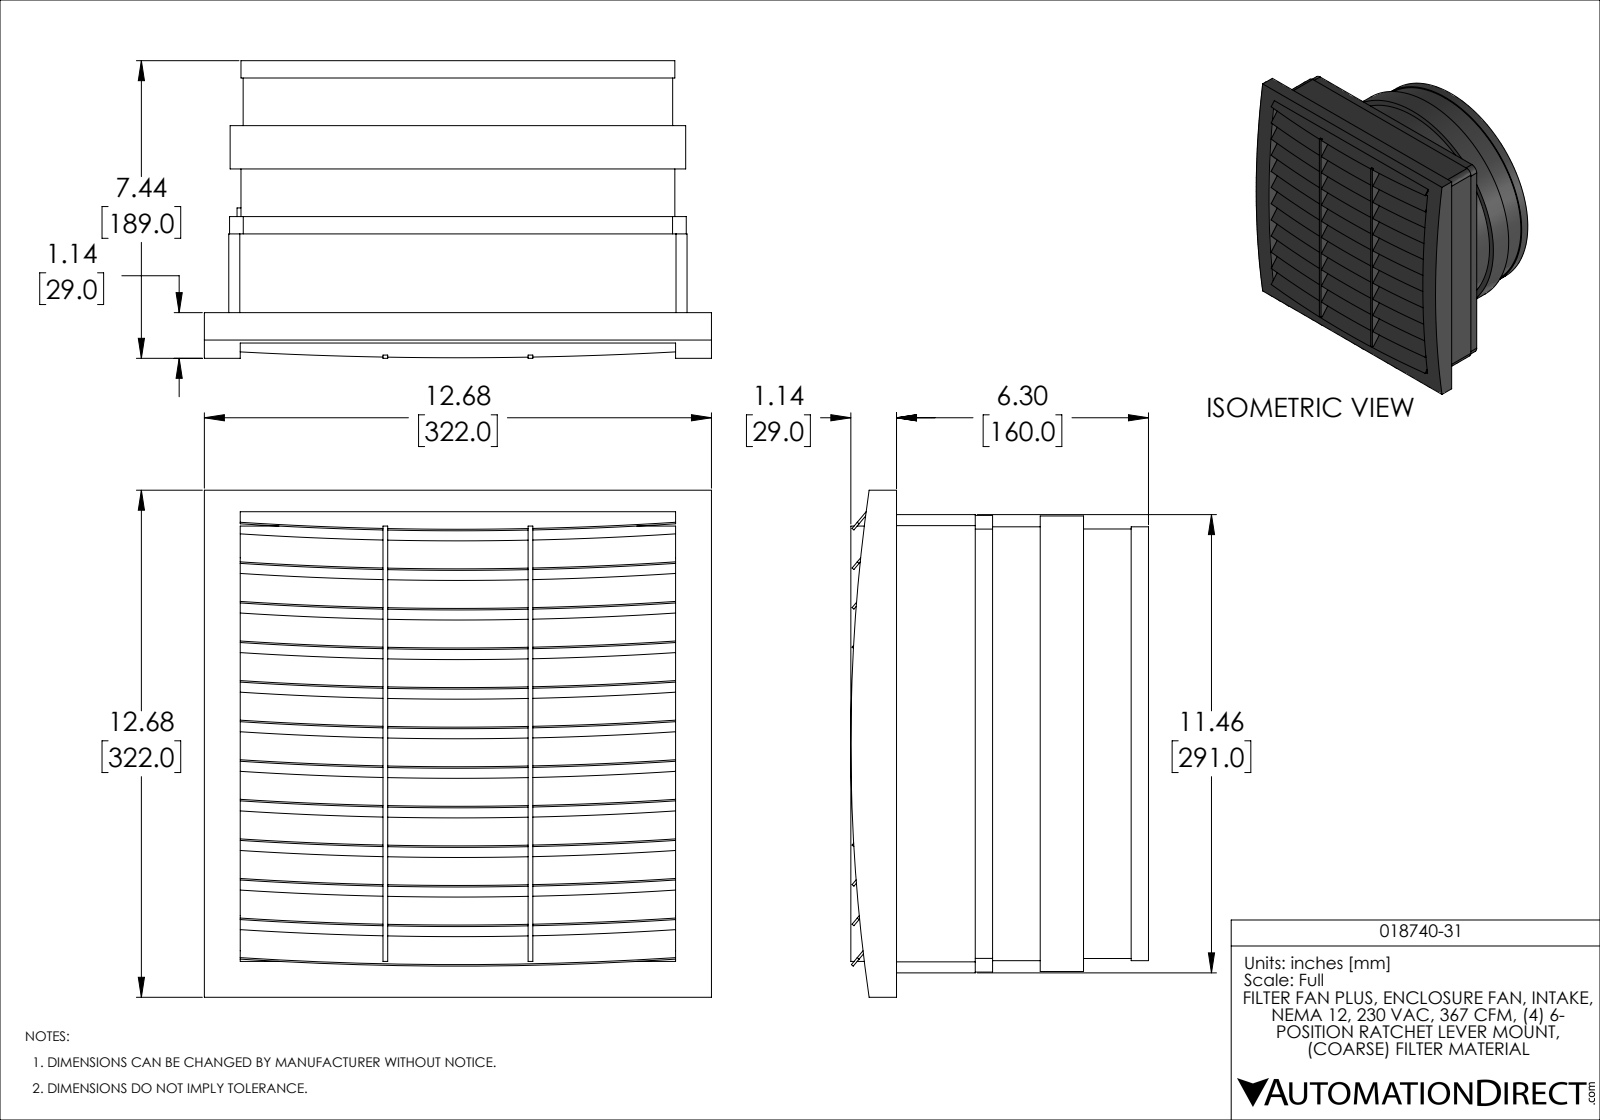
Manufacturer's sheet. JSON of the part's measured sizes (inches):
{"part_name": "PRODUCT_NAME_1", "step_written_by": "ACIS (AUTOMOTIVE_DESIGN_CC2)", "units": "inches", "bodies": {"solids": 1, "faces": 893, "planar": 483, "cylindrical": 410, "other": 0}, "overall_size": [12.677, 12.677, 7.441], "volume_in3": 346.7, "surface_area_in2": 1597, "round_holes": [[3, 1], [3.989, 1], [4.692, 1], [4.979, 1], [5.909, 1], [5.969, 1], [6.958, 1], [7.126, 1], [7.948, 1], [8.344, 1], [9.134, 1], [9.738, 1]], "round_bosses_or_shafts": [[11.389, 1], [10.846, 1], [10.738, 1], [8.698, 1], [8.341, 1], [7.481, 1], [7.352, 1], [6.362, 1]], "partial_cylinders_radius": [[64.96, 23], [4.43, 7], [0.276, 4], [0.343, 4], [1.217, 1], [1.737, 1], [1.915, 1], [44.216, 1]], "face_to_face_distances": [0.636, 1.272, 1.909, 0.591, 2.545, 0.197, 3.181, 0.059, 0.695, 1.331]}
